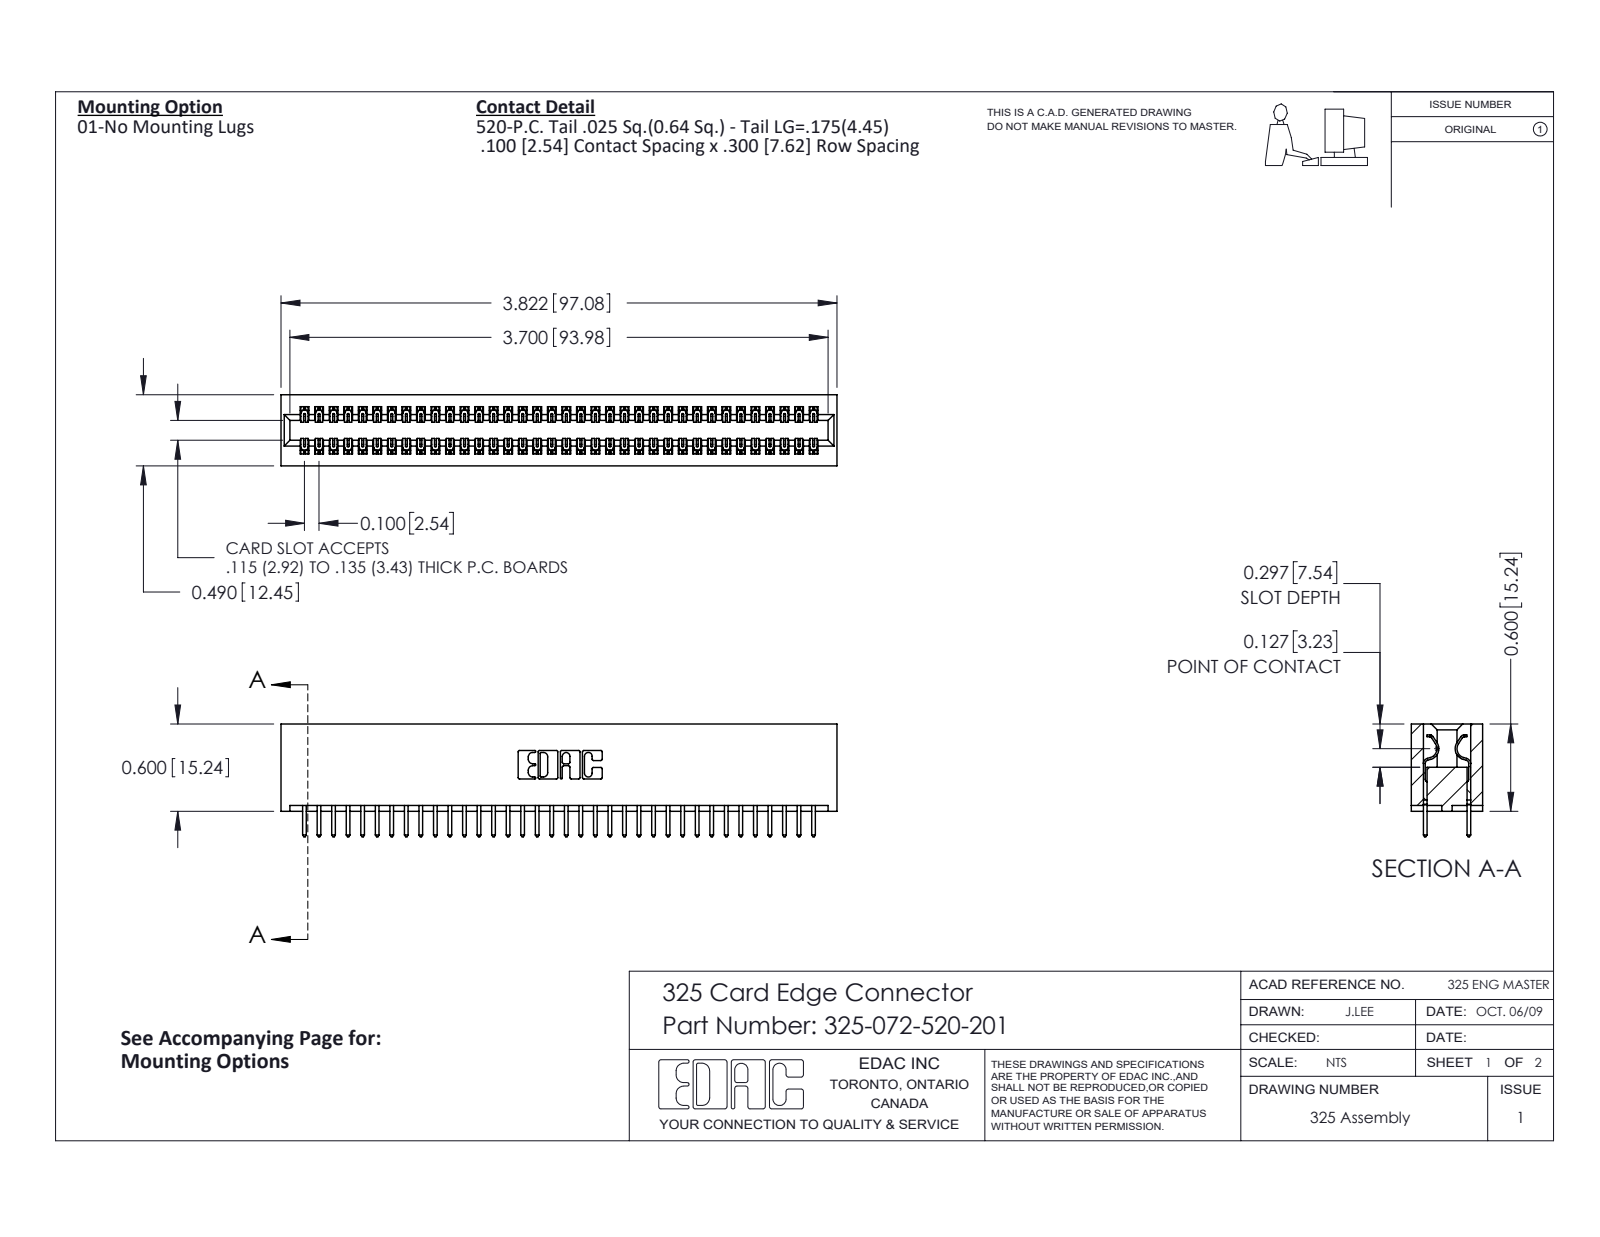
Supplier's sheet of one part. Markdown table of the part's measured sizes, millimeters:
| quantity | value |
| --- | --- |
| part name | 325-072-520-201; 325 Part_Lugless; 325-292-001_325-293-120 |
| STEP written by | SolidWorks 2016 (CONFIG_CONTROL_DESIGN) |
| units | millimeters |
| bodies | 73 solids, 3850 faces (2658 planar, 1192 cylindrical, 0 other) |
| overall size | 97.1 × 19.7 × 12.4 |
| volume | 13 100 mm³ |
| surface area | 16 200 mm² |
| partial cylindrical surfaces (radius × count) | 0.2 × 108, 0.3 × 72, 0.3 × 22, 0.2 × 6, 0.8 × 6, 0.7 × 3, 0.4 × 2, 0.6 × 2 |
| main face-to-face distances | 2.1, 10.3, 7.6, 12.4, 2.7, 9.7, 0.6, 8.3, 14.2, 7 |
